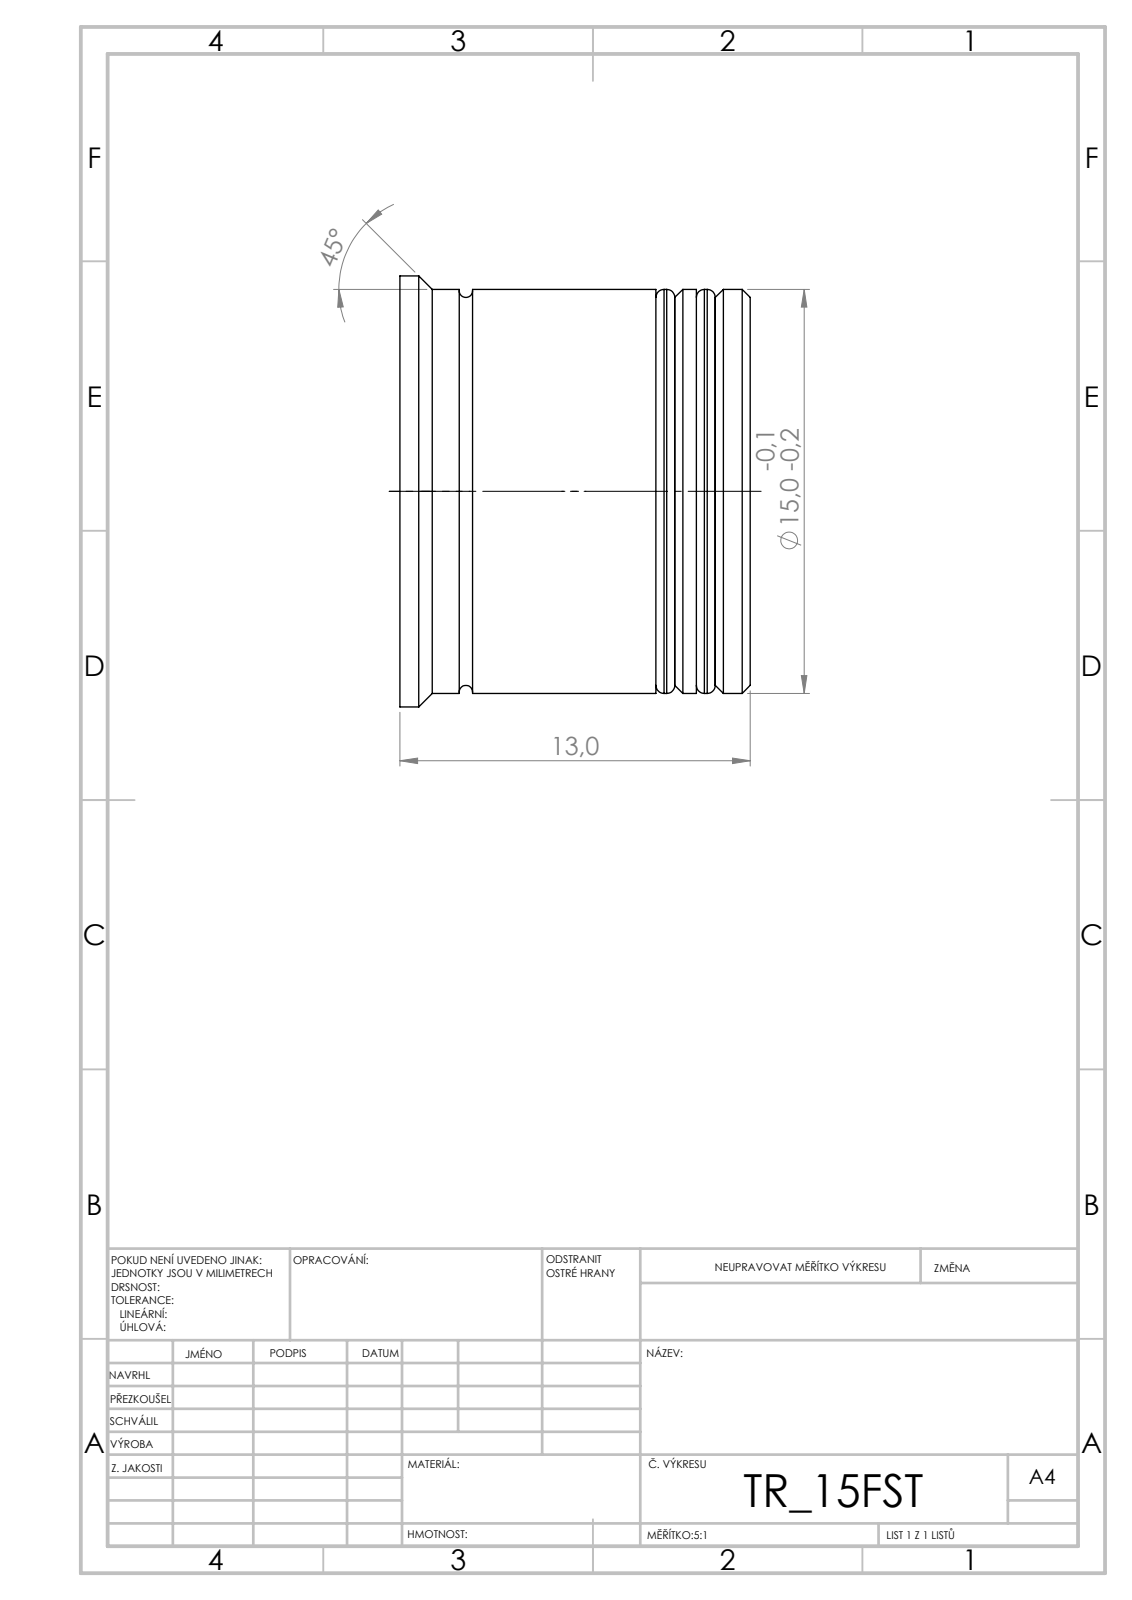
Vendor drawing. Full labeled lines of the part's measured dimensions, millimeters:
STEP written by: SolidWorks 2019 (CONFIG_CONTROL_DESIGN)
Units: millimetres
Bodies: 3 solids, 74 faces (29 planar, 25 cylindrical, 20 other)
Overall size (bounding box): 16 × 16 × 13
Volume: 2 396 mm³ · Surface area: 1 900 mm²
Round bosses / shafts (diameter × count): ⌀16 ×1, ⌀15 ×1, ⌀14.4 ×1
Partial cylindrical surfaces — rounded edges, fillets, slot ends (radius × count): R6 ×1
Main face-to-face distances: 1.5, 0.7, 12, 2.2, 0.8, 1.3, 2, 2.8, 3.5, 10.7
